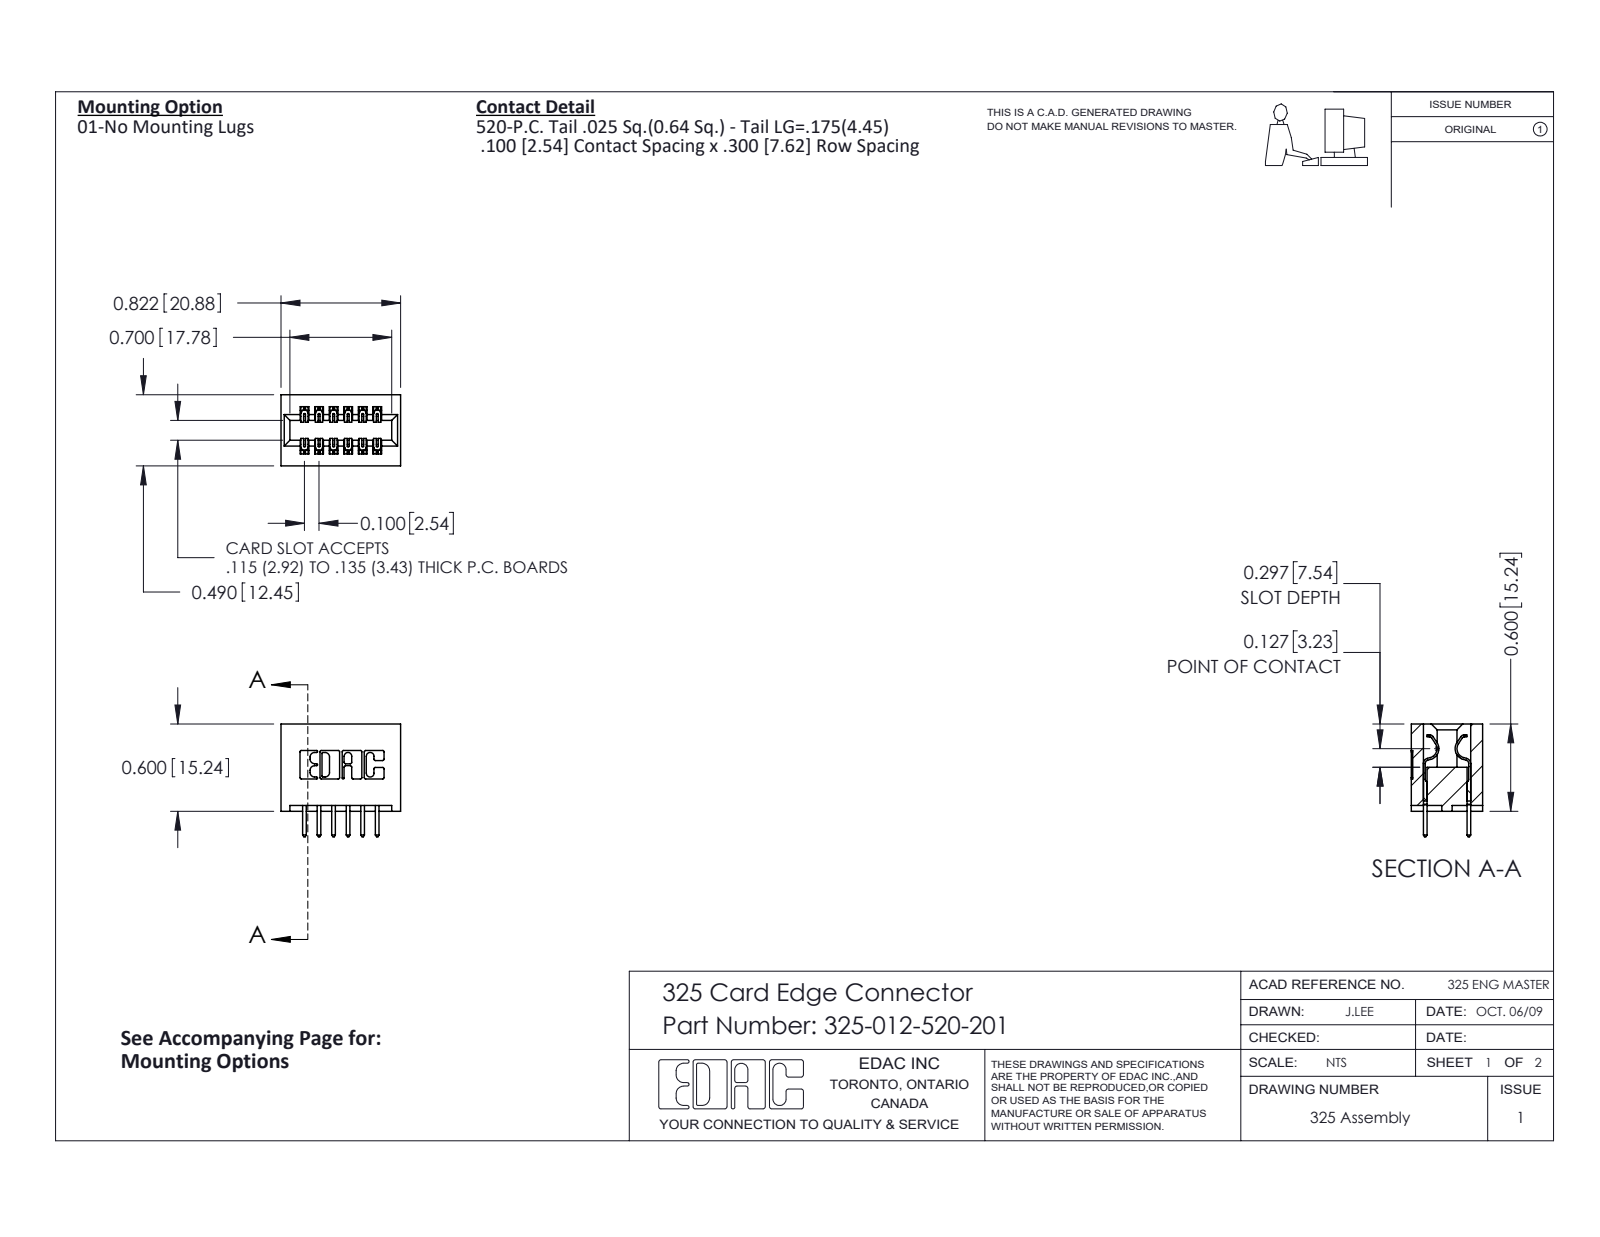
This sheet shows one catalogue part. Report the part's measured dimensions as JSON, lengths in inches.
{"part_name": "325-012-520-201; 325-292-001_325-293-120; 325 Part_Lugless", "step_written_by": "SolidWorks 2016 (CONFIG_CONTROL_DESIGN)", "units": "inches", "bodies": {"solids": 13, "faces": 730, "planar": 498, "cylindrical": 232, "other": 0}, "overall_size": [0.822, 0.775, 0.49], "volume_in3": 0.182, "surface_area_in2": 5.248, "partial_cylinders_radius": [[0.01, 22], [0.006, 18], [0.01, 12], [0.007, 6], [0.031, 6], [0.026, 3], [0.014, 2], [0.022, 2]], "face_to_face_distances": [0.3, 0.1, 0.083, 0.407, 0.2, 0.04, 0.06, 0.49, 0.107, 0.383]}
